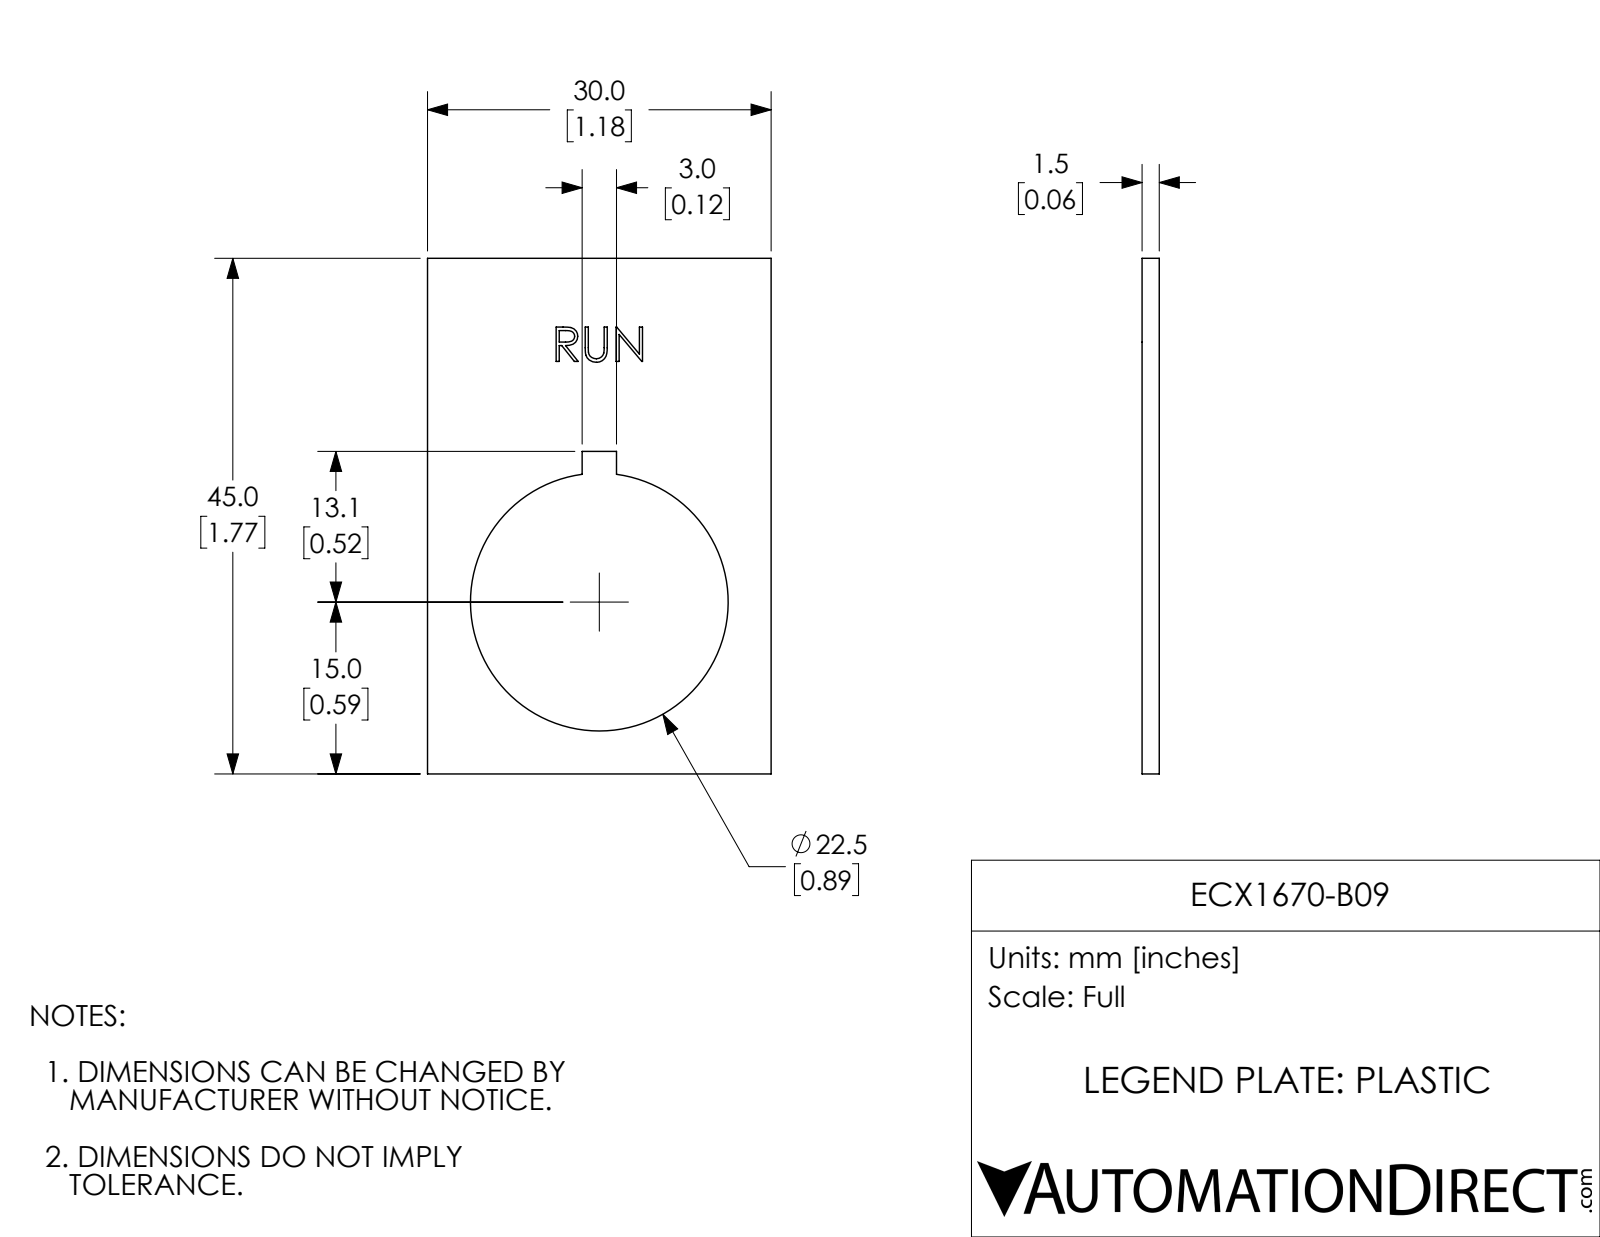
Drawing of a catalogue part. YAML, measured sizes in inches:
part_name: "ECX1670-B09"
step_written_by: "SolidWorks 2017 (AUTOMOTIVE_DESIGN)"
units: inches
bodies: {solids: 1, faces: 55, planar: 40, cylindrical: 3, other: 12}
overall_size: [1.772, 1.181, 0.059]
volume: 0.087
surface_area: 3.459
round_holes:
  - {diameter: 0.886, count: 1}
face_to_face_distances: [0.059, 1.181, 1.772, 0.058, 0.531, 0.65, 1.108, 0.663, 0.118, 0.089]
